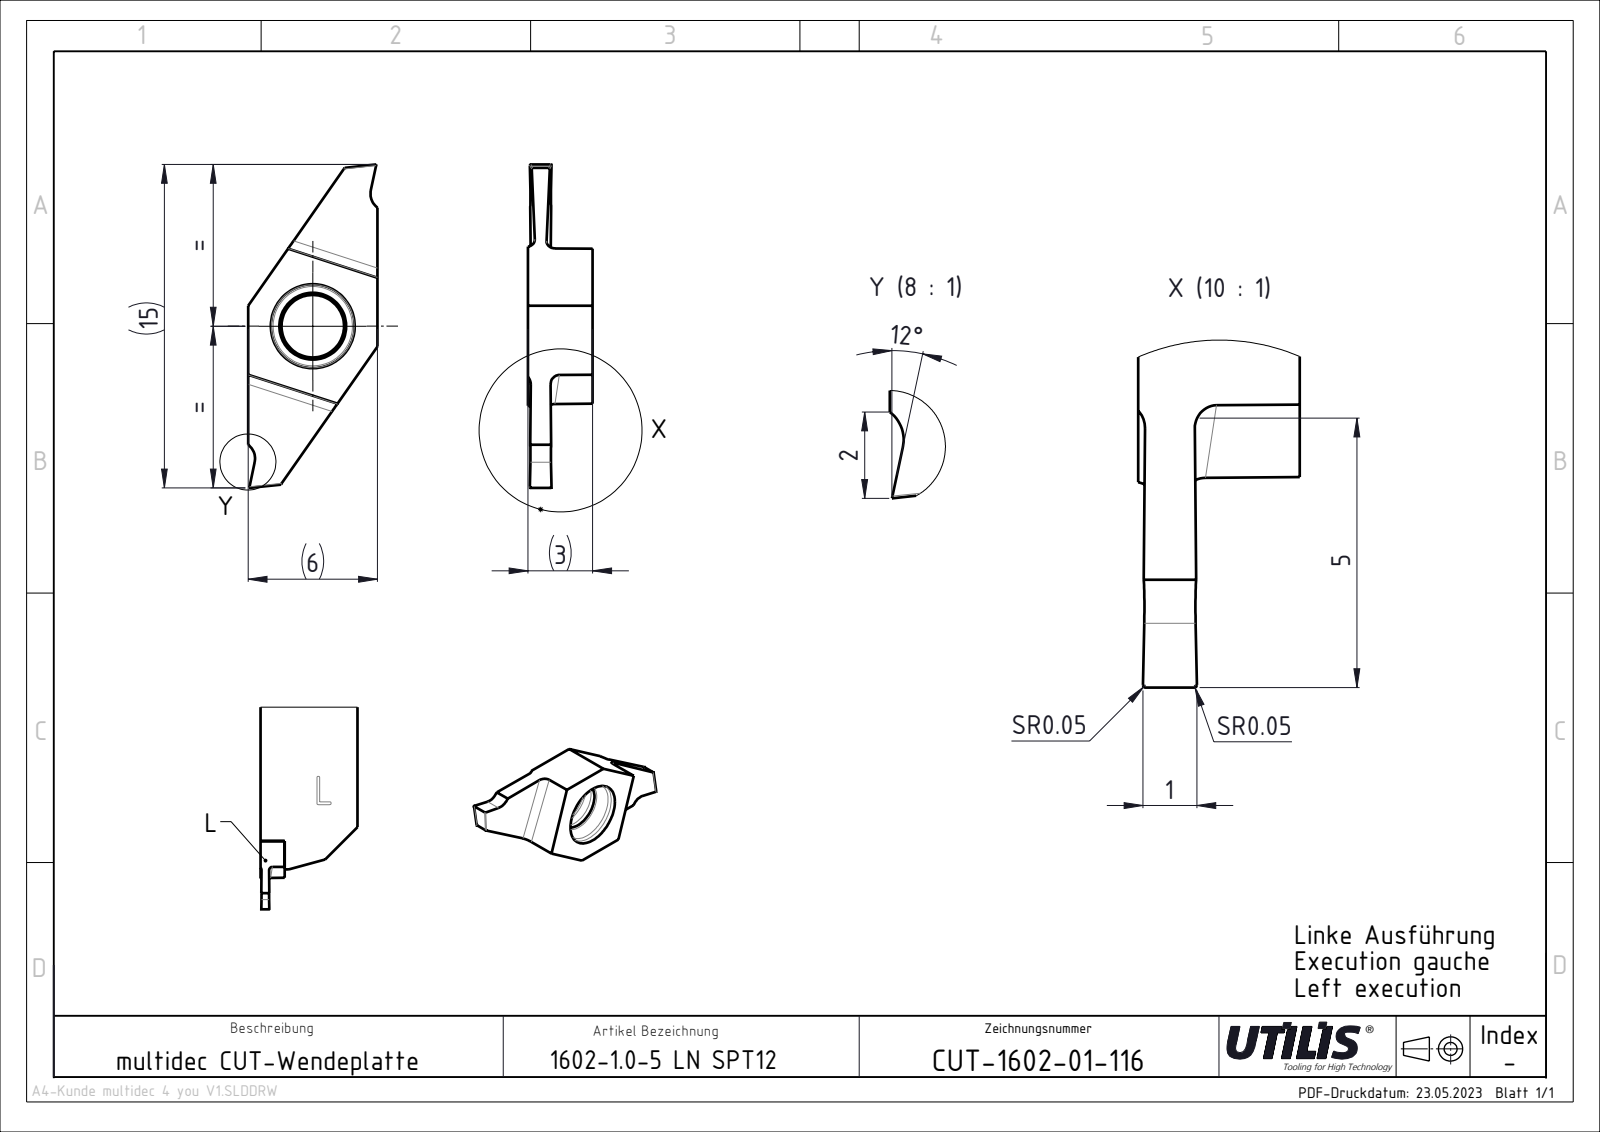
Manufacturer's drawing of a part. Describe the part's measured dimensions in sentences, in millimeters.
The part is named "1602-CUT-1602-01-116 stp". Its 3-D file was written by "SolidWorks 2022 (AUTOMOTIVE_DESIGN)". It is 1 solid with 23 faces: 14 planar, 9 cylindrical and 0 other. Overall it measures 15 by 6 by 3 millimeters. Its volume is 105 cubic millimeters and its surface area 210 square millimeters. Round holes: 1 of diameter 2.9. Partial cylindrical surfaces (rounded edges, fillets, slot ends): 4 of radius 0.4. The main face-to-face distances are 6, 3, 0.84, 15.
